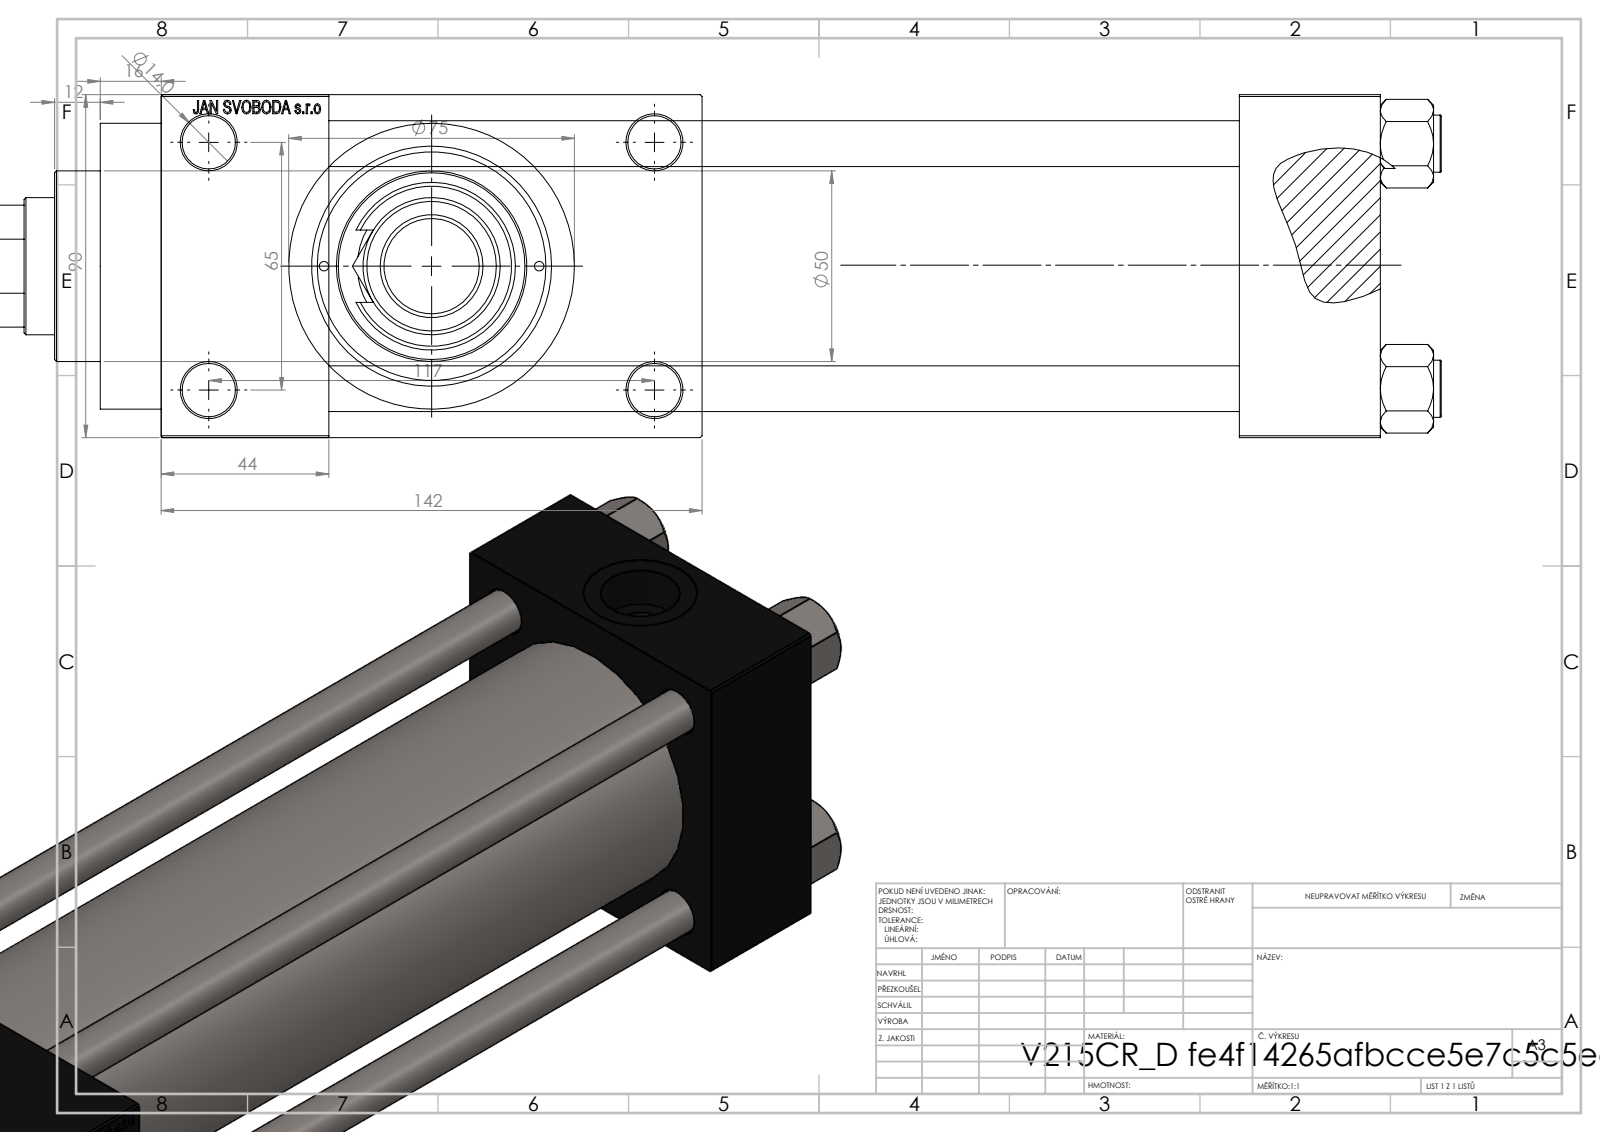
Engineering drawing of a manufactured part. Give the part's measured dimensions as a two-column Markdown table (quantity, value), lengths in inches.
| quantity | value |
| --- | --- |
| part name | V215CR_D_Body; MFA; NUT_M5_D; FEMALE_PART_FOR_DFA (+3 more) |
| STEP written by | SolidWorks 2019 (CONFIG_CONTROL_DESIGN) |
| units | inches |
| bodies | 13 solids, 1197 faces (527 planar, 106 cylindrical, 564 other) |
| overall size | 19.429 × 5.591 × 3.543 |
| volume | 97.33 in³ |
| surface area | 538.2 in² |
| round holes (diameter × count) | 0.472 × 4, 0.551 × 4, 0.098 × 2, 0.276 × 2, 0.825 × 2, 1.181 × 2, 1.004 × 1, 1.535 × 1, 1.969 × 1, 2.362 × 1, 2.48 × 1 |
| round bosses / shafts (diameter × count) | 0.591 × 4, 2.953 × 1, 2.717 × 1, 1.732 × 1, 1.417 × 1, 1.102 × 1, 1.063 × 1, 0.984 × 1 |
| partial cylindrical surfaces (radius × count) | 0.374 × 1, 0.591 × 1, 0.689 × 1 |
| main face-to-face distances | 3.543, 9.409, 1.457, 10.866, 12.598, 11.142, 1.732, 1.024, 4.567, 5.591 |
| hole center spacings | 1.037, 1.275, 1.748, 1.79, 2.531, 2.635, 2.694, 2.748 |
